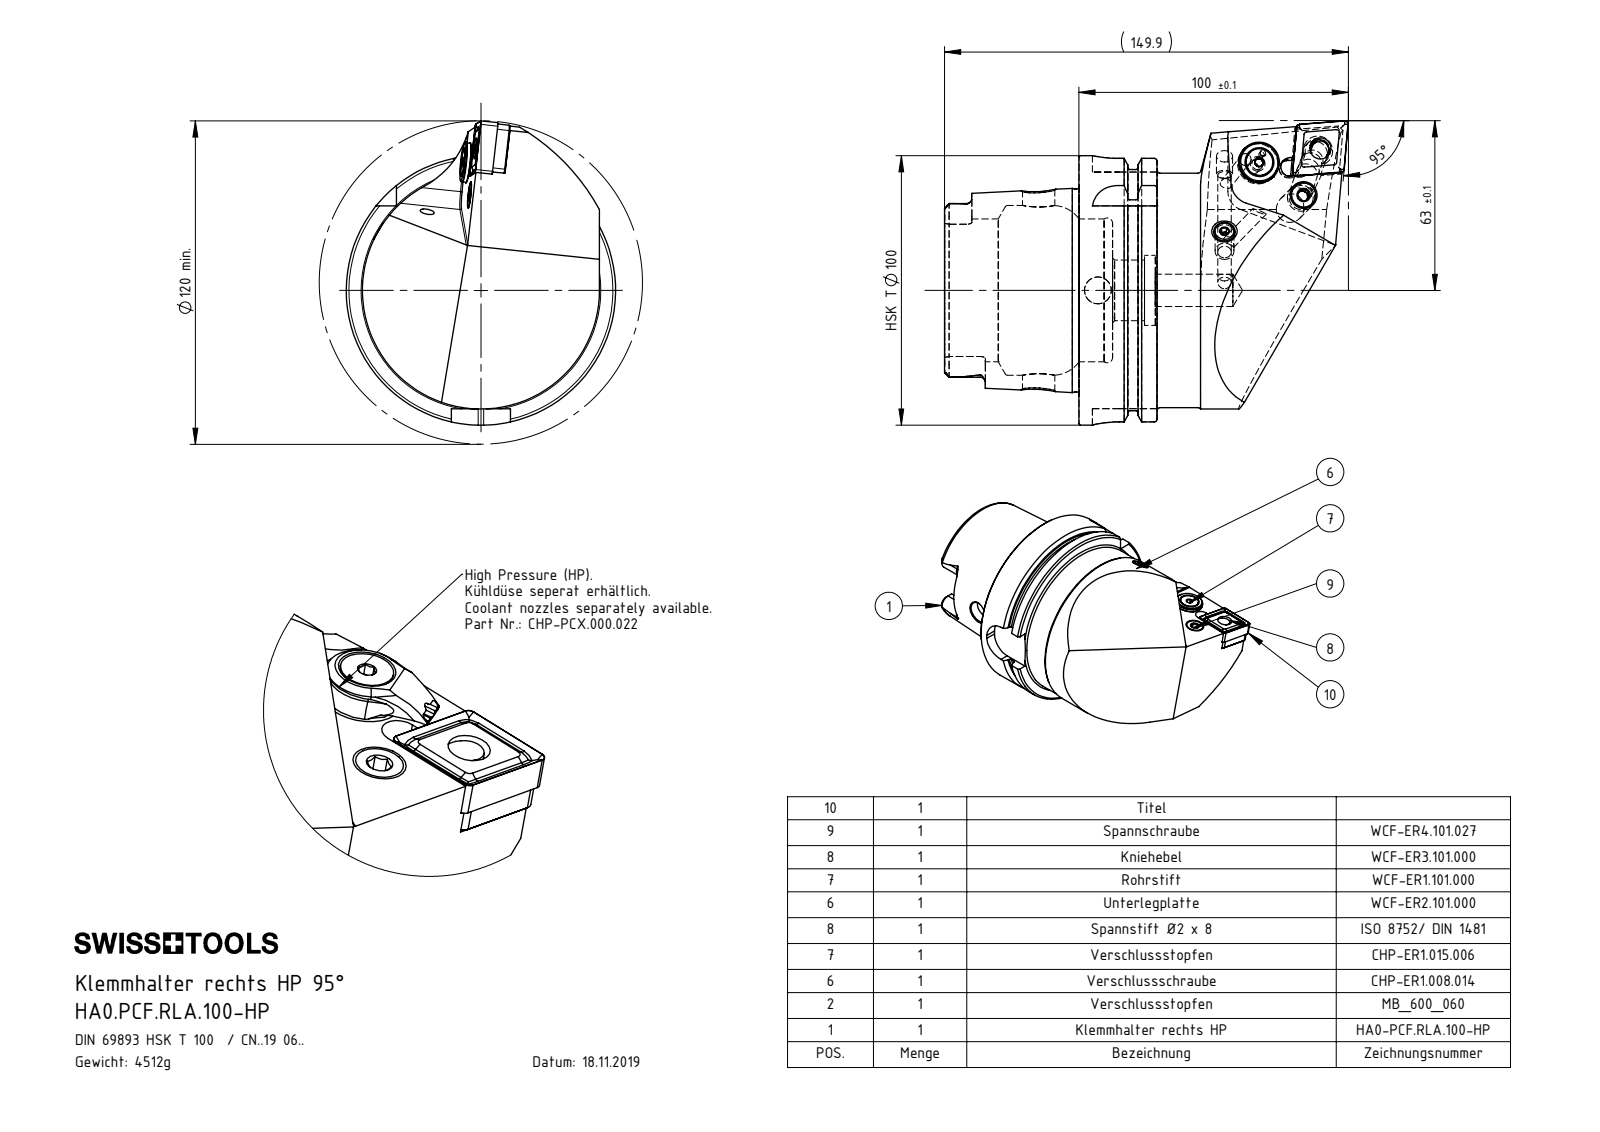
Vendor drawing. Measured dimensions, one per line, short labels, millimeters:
name: HA0-PCF.RLA.100-HP_A_Fertigbearbeitung; CHP-ER1.015.006; DIN 3771 - 13x1; WCF-ER1.101.000 (+8 more)
written by: SolidWorks 2017 (AUTOMOTIVE_DESIGN)
unit: mm
bodies: 13 solids, 395 faces (165 planar, 90 cylindrical, 140 other)
size: 149.81 × 112.92 × 100
volume: 573 284 mm³; area: 78 489 mm²
holes: 3× ⌀5, 2× ⌀4.2, 2× ⌀12, 1× ⌀1.2, 1× ⌀2, 1× ⌀2.5, 1× ⌀3, 1× ⌀5.2, 1× ⌀7, 1× ⌀7.94, 1× ⌀9, 1× ⌀9.6
bosses: 2× ⌀10, 1× ⌀100, 1× ⌀91.95, 1× ⌀87, 1× ⌀75.26, 1× ⌀15, 1× ⌀13.4, 1× ⌀9.9
rounds: 6× R1.9, 4× R1.2, 4× R1.8, 4× R10, 3× R4, 2× R0.5, 2× R4.7, 2× R4.83
face distances: 12.45, 28.95, 16.5, 49.9, 62.35, 78.85, 6.05, 87.8, 0.65, 78.2
hole spacings: 4.5, 20.51, 20.98, 21.22, 21.67, 23.59, 23.86, 0.32
